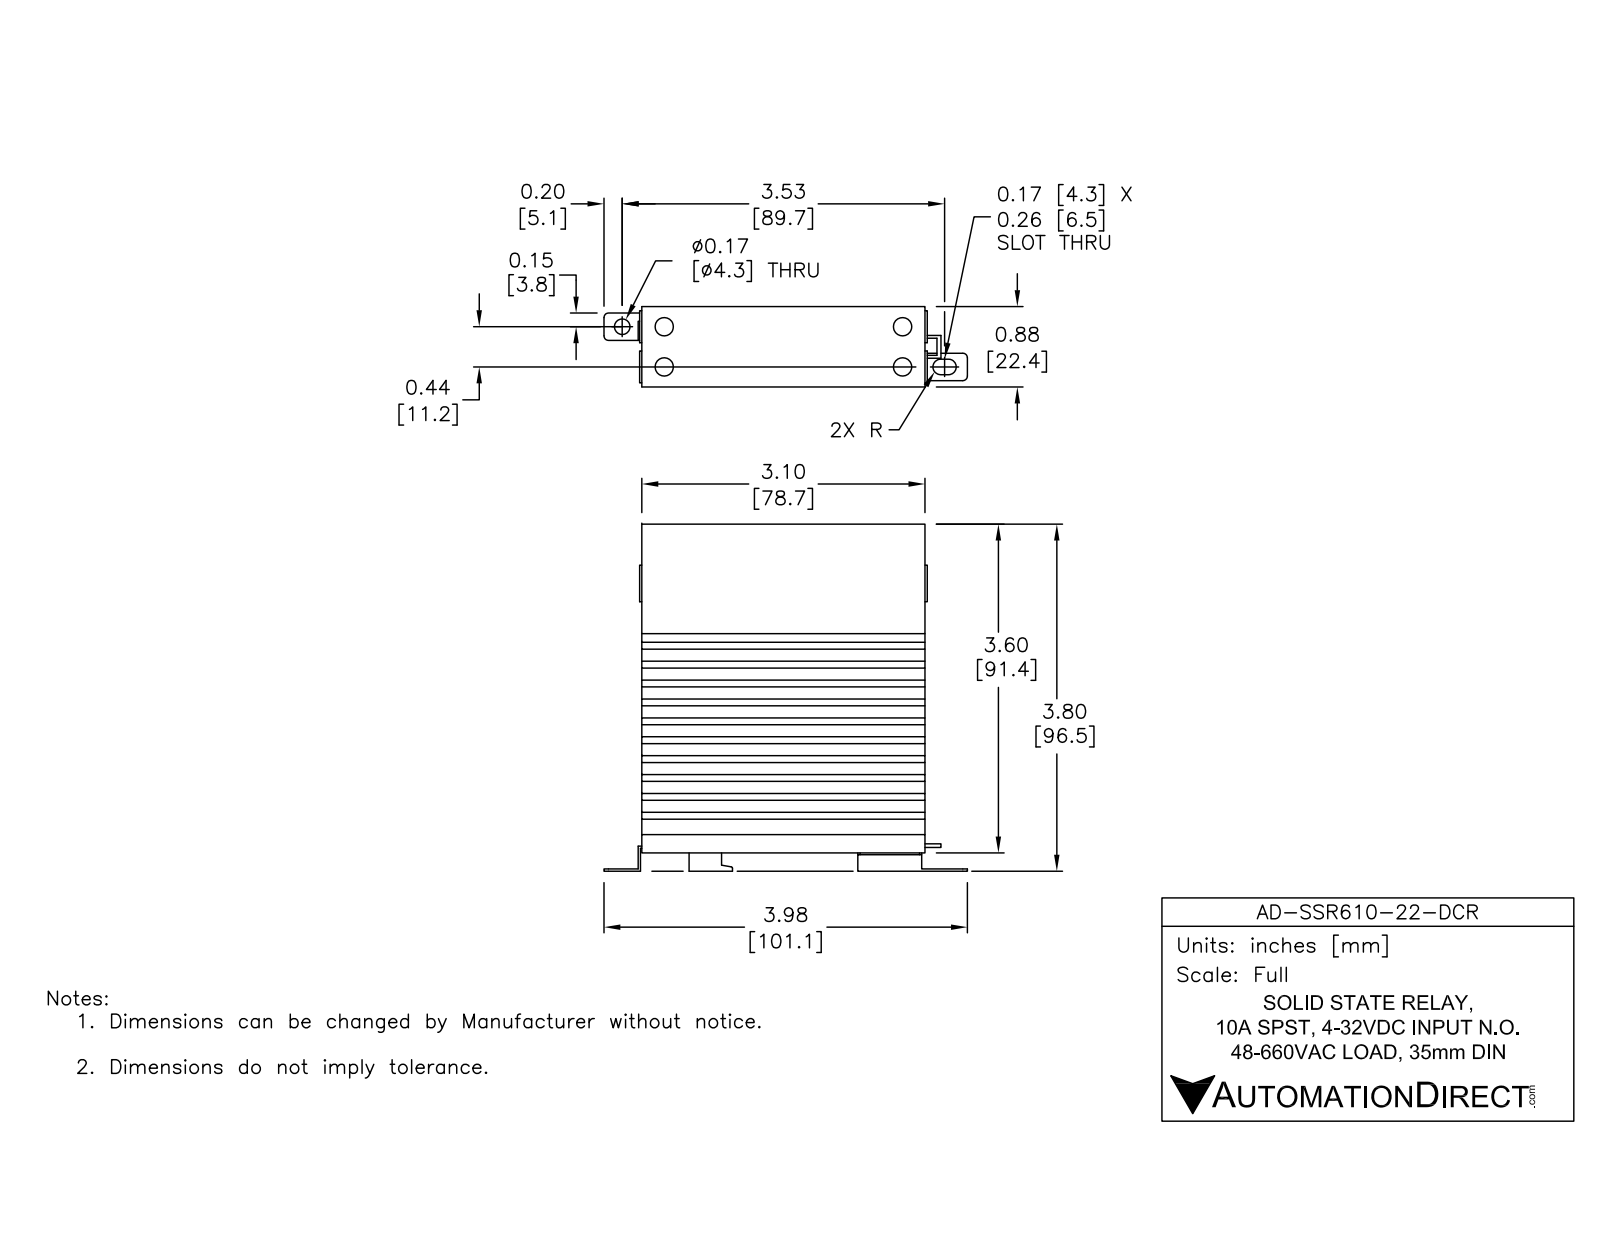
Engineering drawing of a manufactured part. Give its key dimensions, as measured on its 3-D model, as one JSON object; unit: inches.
{"part_name": "AD-SSR610-22-DCR", "step_written_by": "SolidWorks 2014 (AUTOMOTIVE_DESIGN)", "units": "inches", "bodies": {"solids": 1, "faces": 215, "planar": 195, "cylindrical": 20, "other": 0}, "overall_size": [3.98, 3.8, 0.88], "volume_in3": 7.136, "surface_area_in2": 74.91, "round_holes": [[0.2, 4], [0.17, 1]], "partial_cylinders_radius": [[0.05, 6], [0.085, 2], [0.015, 1]], "face_to_face_distances": [0.62, 0.207, 0.827, 0.414, 0.132, 0.489, 0.339, 0.413, 0.075, 0.207], "hole_center_spacings": [0.44, 2.61, 2.647, 0.46, 0.637, 3.07, 3.102]}
